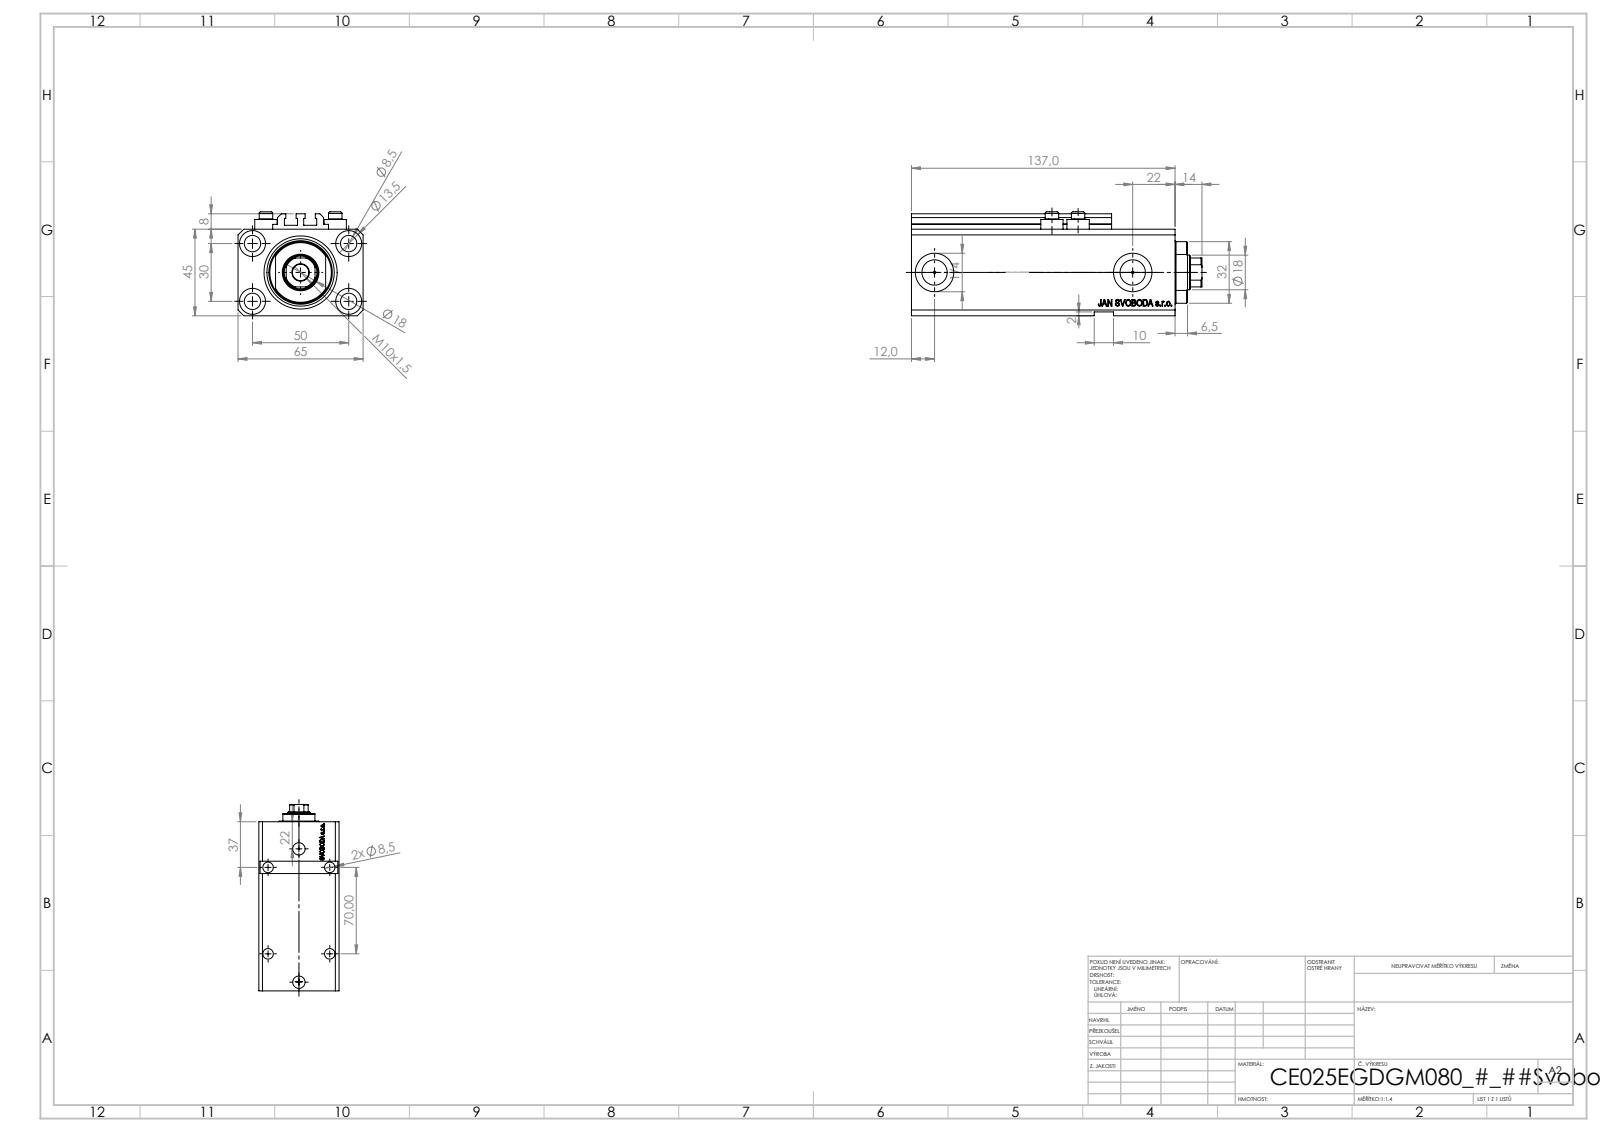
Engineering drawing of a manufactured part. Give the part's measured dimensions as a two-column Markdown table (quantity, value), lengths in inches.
| quantity | value |
| --- | --- |
| part name | V250CE_VC_E; V250CE_C_VCP; V250CE_E_Body; ALLEN BOLT V250CE |
| STEP written by | SolidWorks 2019 (CONFIG_CONTROL_DESIGN) |
| units | inches |
| bodies | 8 solids, 1103 faces (515 planar, 158 cylindrical, 430 other) |
| overall size | 5.945 × 2.559 × 2.126 |
| volume | 21.17 in³ |
| surface area | 146.8 in² |
| round holes (diameter × count) | 0.335 × 9, 0.049 × 4, 0.157 × 4, 0.531 × 4, 0.394 × 2, 0.518 × 2, 0.787 × 2, 0.709 × 1, 0.984 × 1, 1.496 × 1 |
| round bosses / shafts (diameter × count) | 0.457 × 4, 0.276 × 4 |
| partial cylindrical surfaces (radius × count) | 0.008 × 10, 0.335 × 1, 0.63 × 1 |
| main face-to-face distances | 1.772, 2.559, 1.85, 0.079, 4.843, 0.098, 0.551, 0.394, 0.803, 5.394 |
| hole center spacings | 1.148, 1.969, 0.535, 0.595, 1.098, 1.181, 1.323, 1.324 |
